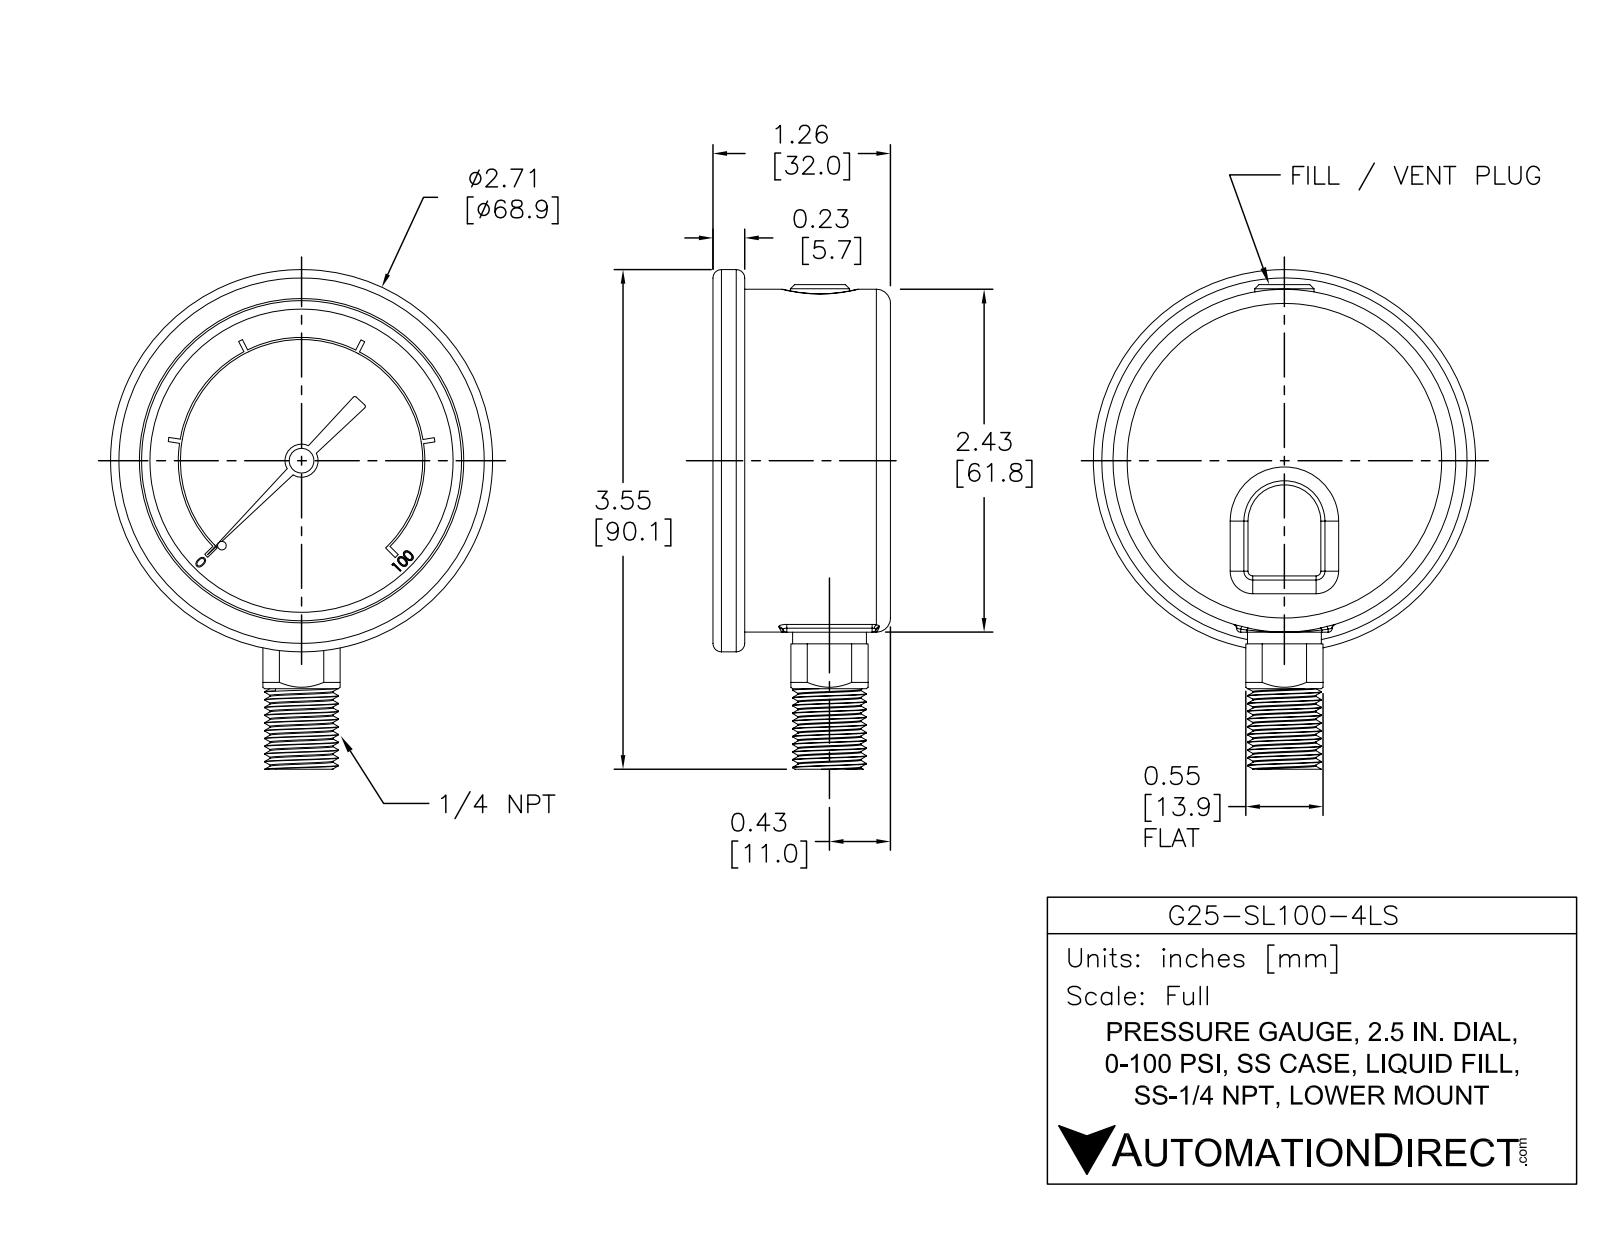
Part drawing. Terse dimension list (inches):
name: G25-SL100-4LS
written by: SolidWorks 2021 (AUTOMOTIVE_DESIGN)
unit: in
bodies: 1 solid, 343 faces (195 planar, 85 cylindrical, 63 other)
size: 3.546 × 2.713 × 1.26
volume: 5.273 in³; area: 24.68 in²
holes: 1× ⌀0.027, 1× ⌀0.071, 1× ⌀0.119, 1× ⌀2.272
bosses: 1× ⌀2.713, 1× ⌀2.433, 1× ⌀0.524, 1× ⌀0.42, 1× ⌀0.235, 1× ⌀0.176, 1× ⌀0.14, 1× ⌀0.041
rounds: 9× R0.03, 3× R0.1, 2× R0.015, 1× R0.316, 1× R0.86, 1× R0.875
face distances: 1.01, 1.26, 0.25, 1.035, 0.025, 0.225, 0.1, 0.91, 0.935, 1.16
hole spacings: 0.067
